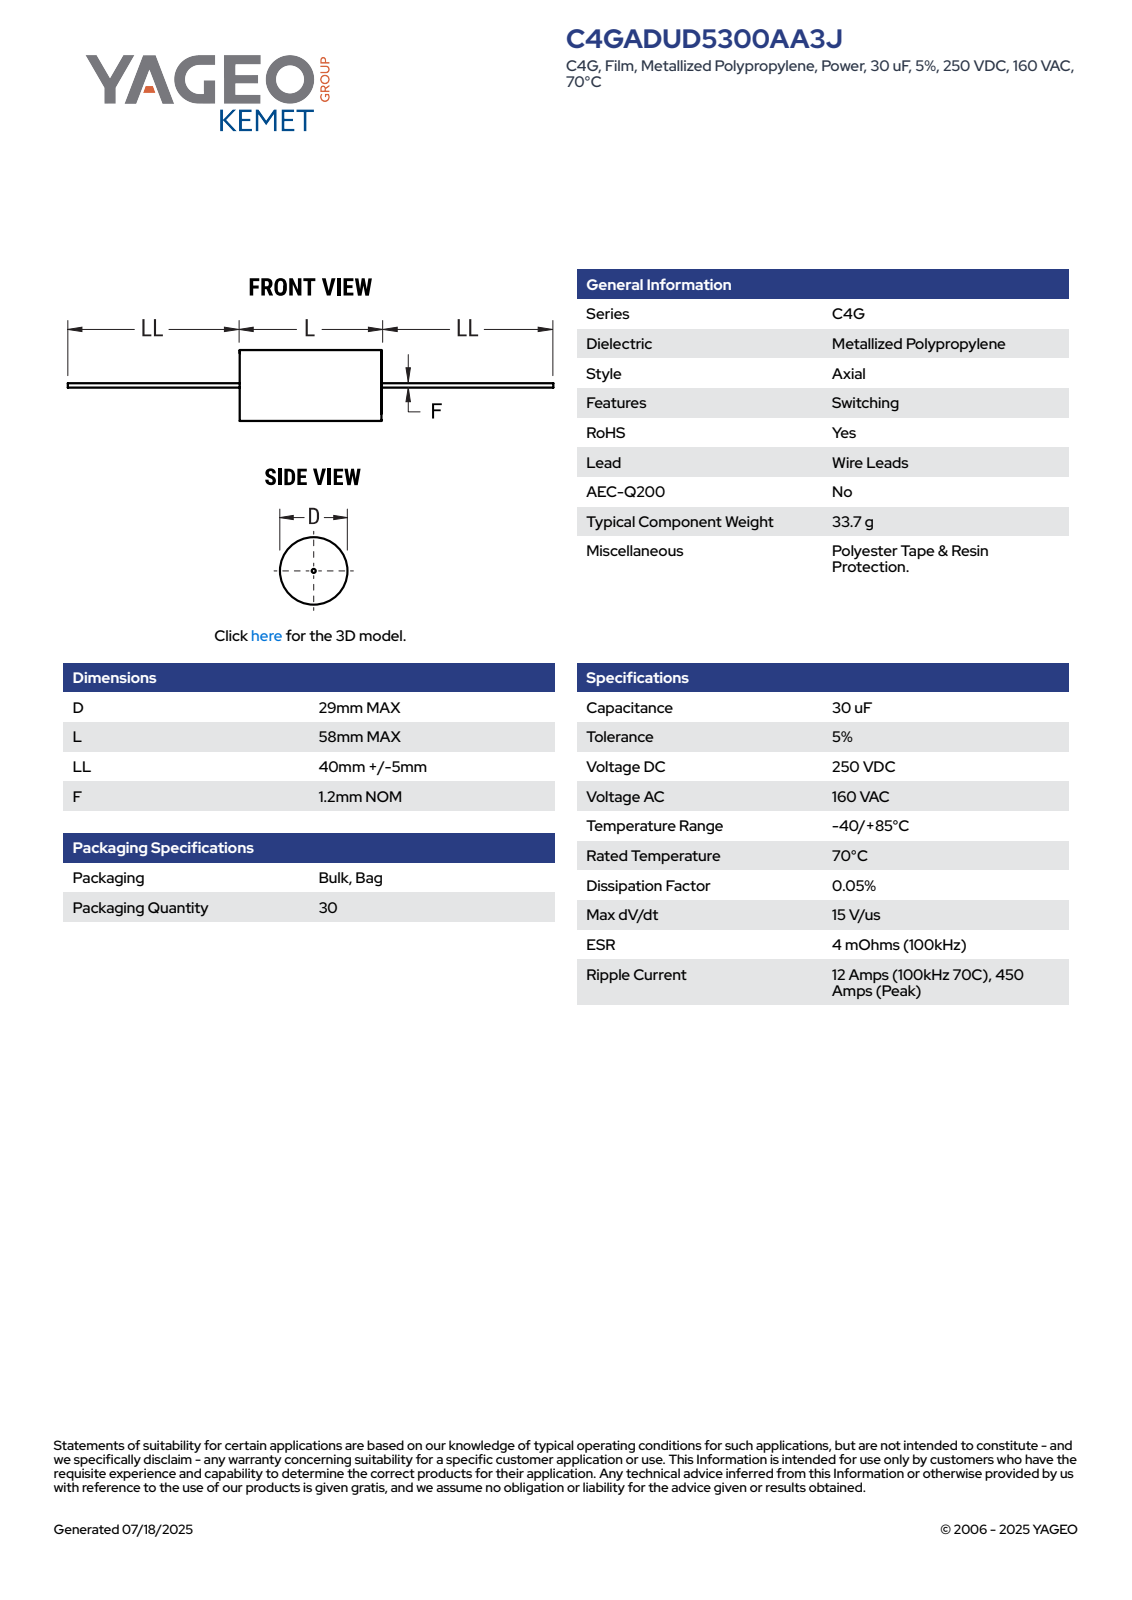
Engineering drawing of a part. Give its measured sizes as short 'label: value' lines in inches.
name: CFP_ACWF_29X58_D29L58LL45F1.2
written by: SolidWorks 2014 (AUTOMOTIVE_DESIGN)
unit: in
bodies: 2 solids, 87 faces (28 planar, 28 cylindrical, 31 other)
size: 5.827 × 1.142 × 1.142
volume: 2.344 in³; area: 12.81 in²
bosses: 1× ⌀1.142, 1× ⌀0.047
rounds: 1× R0.57
face distances: 2.284, 2.283, 1.772, 4.055, 1.771, 5.827, 4.056
